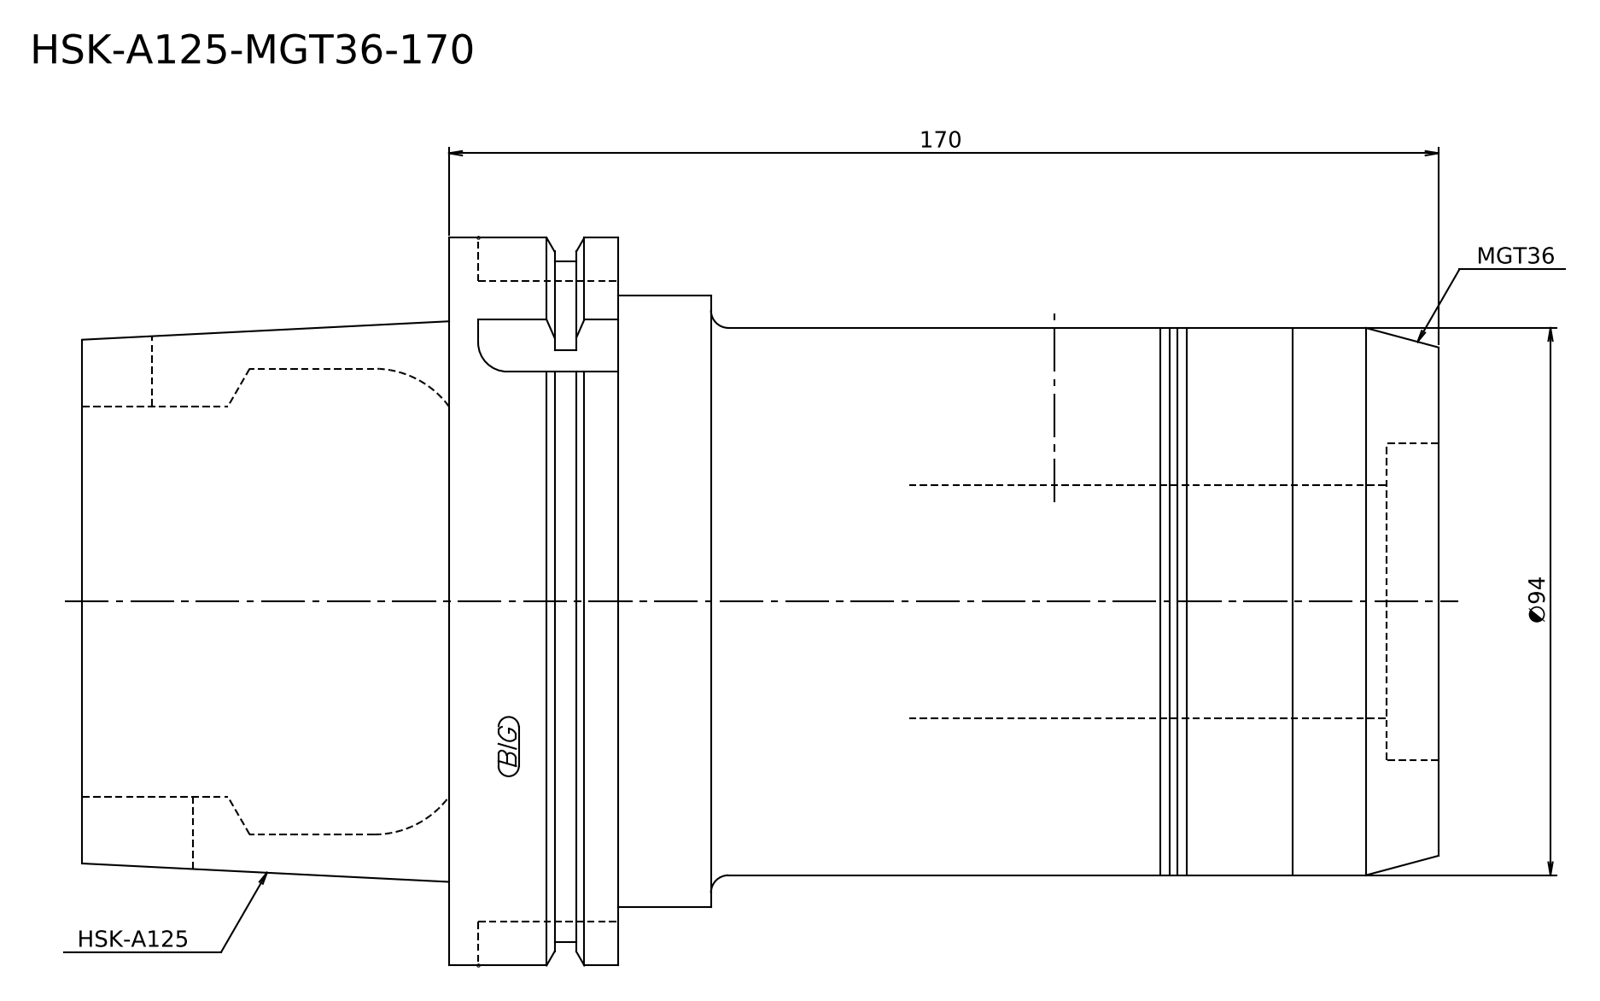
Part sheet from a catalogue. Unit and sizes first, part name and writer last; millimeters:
Units: millimetres
Overall size (bounding box): 233 × 125 × 125
Round bosses / shafts (diameter × count): ⌀125 ×1, ⌀117 ×1, ⌀105 ×1, ⌀94 ×1
Main face-to-face distances: 233, 170, 63, 141, 29, 92, 125, 16, 45, 108
Volume: 1 779 000 mm³ · Surface area: 96 337 mm²
Bodies: 1 solid, 17 faces (7 planar, 5 cylindrical, 5 other)
STEP written by: Kubotek KeyCreator 2011 V10.0.2 (22737) (automotive_design)
